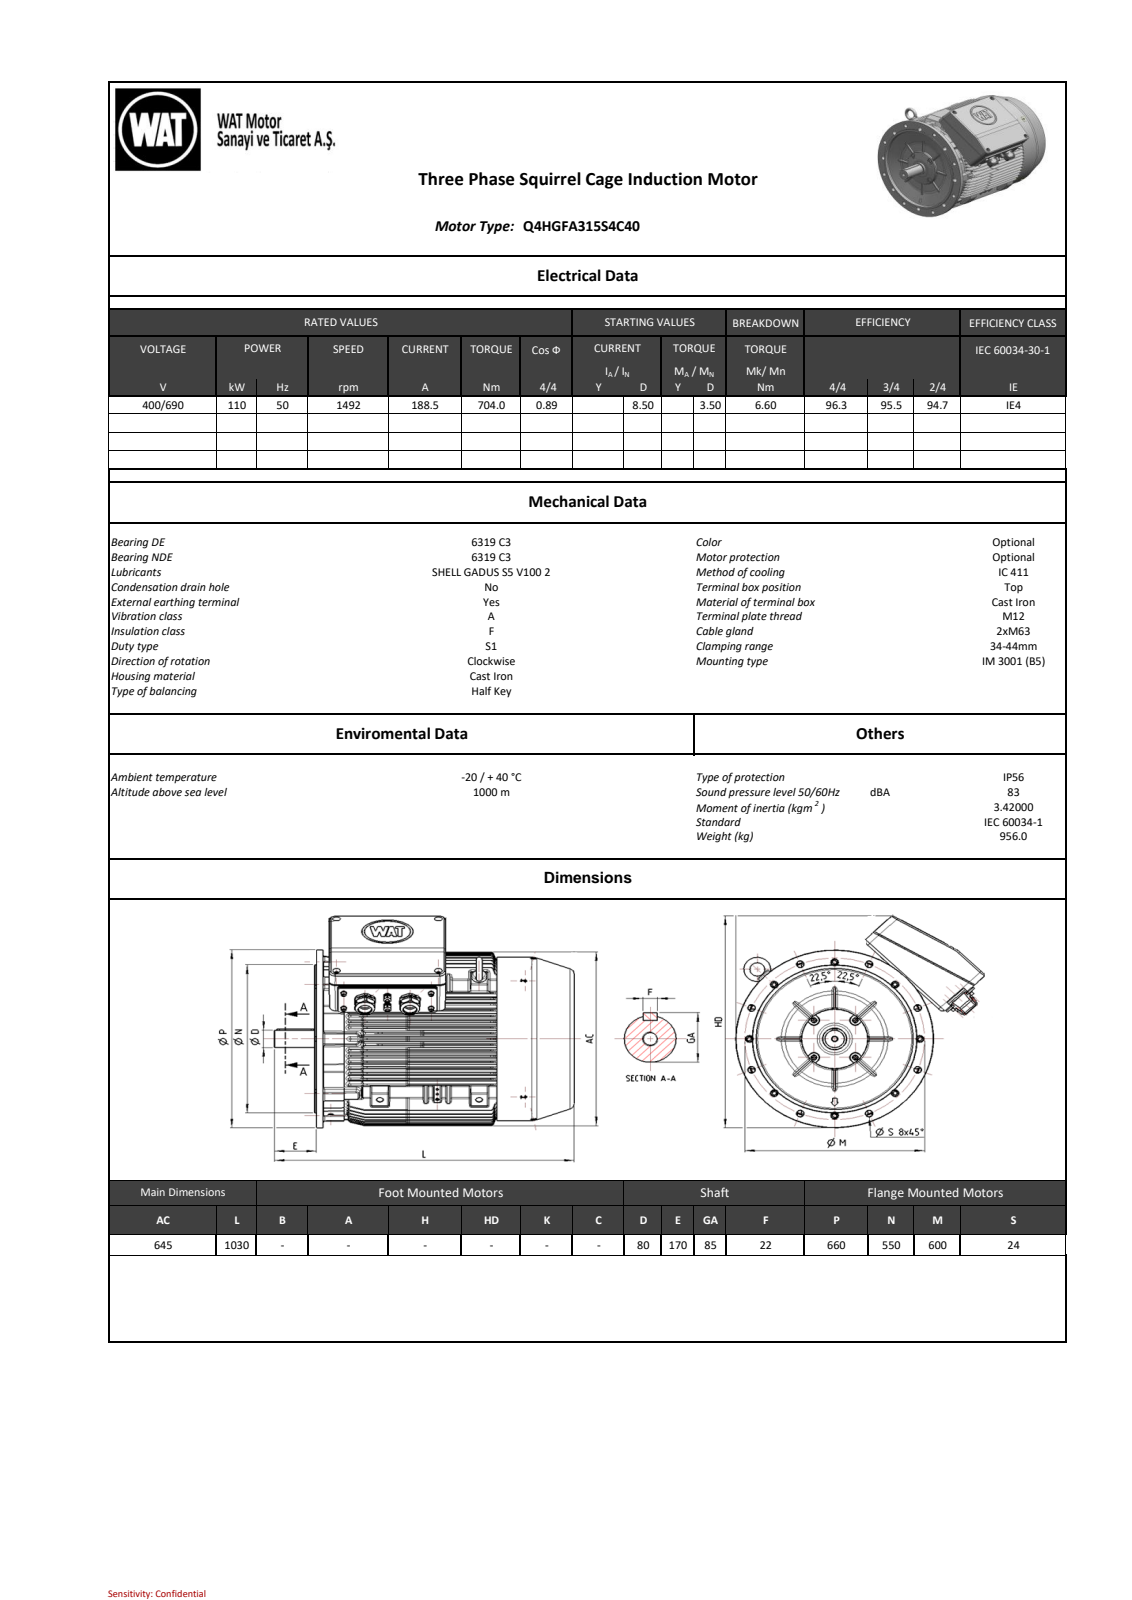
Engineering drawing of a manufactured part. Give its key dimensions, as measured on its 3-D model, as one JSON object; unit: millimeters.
{"part_name": "26009910674F4pi8", "step_written_by": "SIEMENS PLM Software NX 11.0 (AUTOMOTIVE_DESIGN)", "units": "millimeters", "bodies": {"solids": 0, "faces": 6633, "planar": 3448, "cylindrical": 1184, "other": 2001}, "overall_size": [1030, 829.19, 785.69], "round_holes": [[24, 8], [26, 8], [20, 7], [8.5, 4], [9, 4], [22, 4], [4, 2], [8, 2], [12, 2], [12.1, 2], [15, 2], [21, 2]], "round_bosses_or_shafts": [[20, 8], [16, 8], [10, 4], [64.8, 2], [50, 2], [660, 1], [607, 1], [565, 1]], "partial_cylinders_radius": [[6, 460], [3, 158], [2.09, 66], [2.61, 61], [0.8, 36], [10, 26], [1.5, 24], [0.4, 16]], "face_to_face_distances": [117, 305.15, 20.71, 743, 41.51, 284.35, 20.8, 263.64, 1.5, 115.5], "hole_center_spacings": [486.48, 79.06, 115.07, 115.08, 218.13, 300, 325.24, 325.26]}
